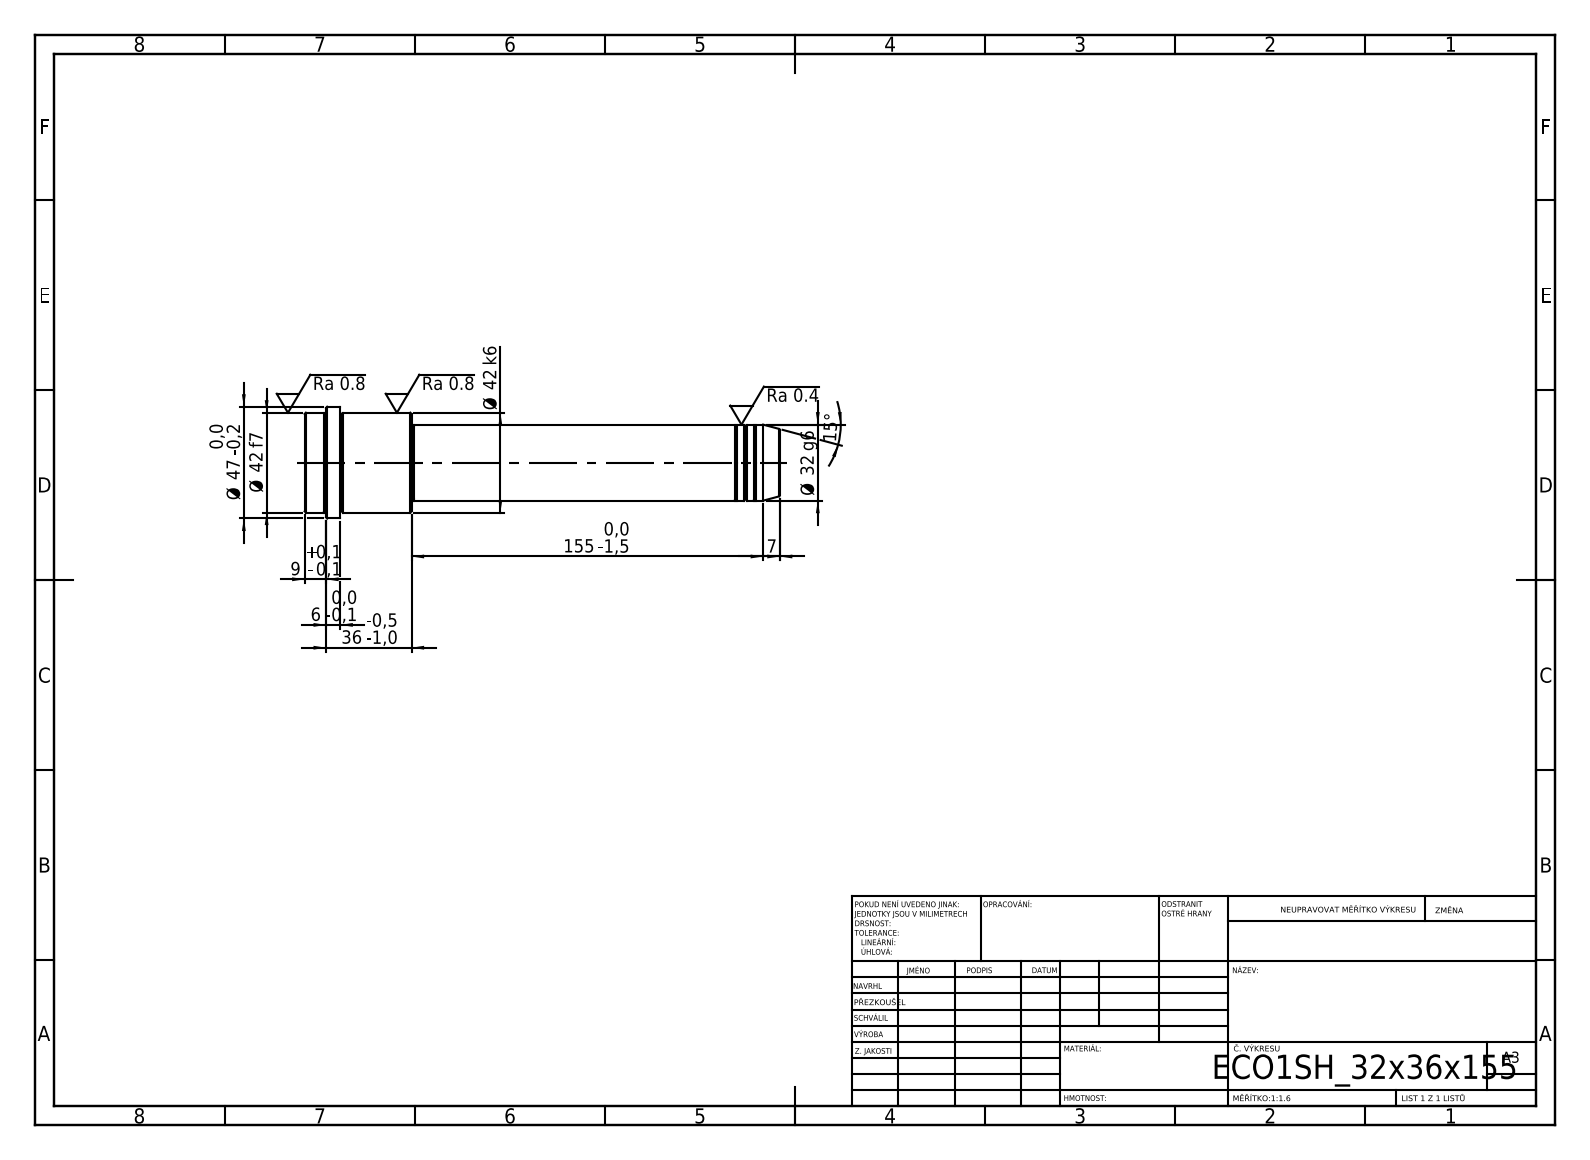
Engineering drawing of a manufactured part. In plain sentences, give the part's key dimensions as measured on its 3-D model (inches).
Its 3-D file was written by "SolidWorks 2019 (CONFIG_CONTROL_DESIGN)". It is 1 solid with 52 faces: 6 planar, 16 cylindrical and 30 other. Overall it measures 7.874 by 1.85 by 1.85 inches. Its volume is 11.48 cubic inches and its surface area 39 square inches. Round bosses or shafts: 1 of diameter 1.85, 1 of diameter 1.654, 1 of diameter 1.26, 1 of diameter 1.22. The main face-to-face distances are 7.874, 6.102, 1.772, 7.283, 1.181, 0.591, 7.52, 1.417, 0.236, 0.354.
